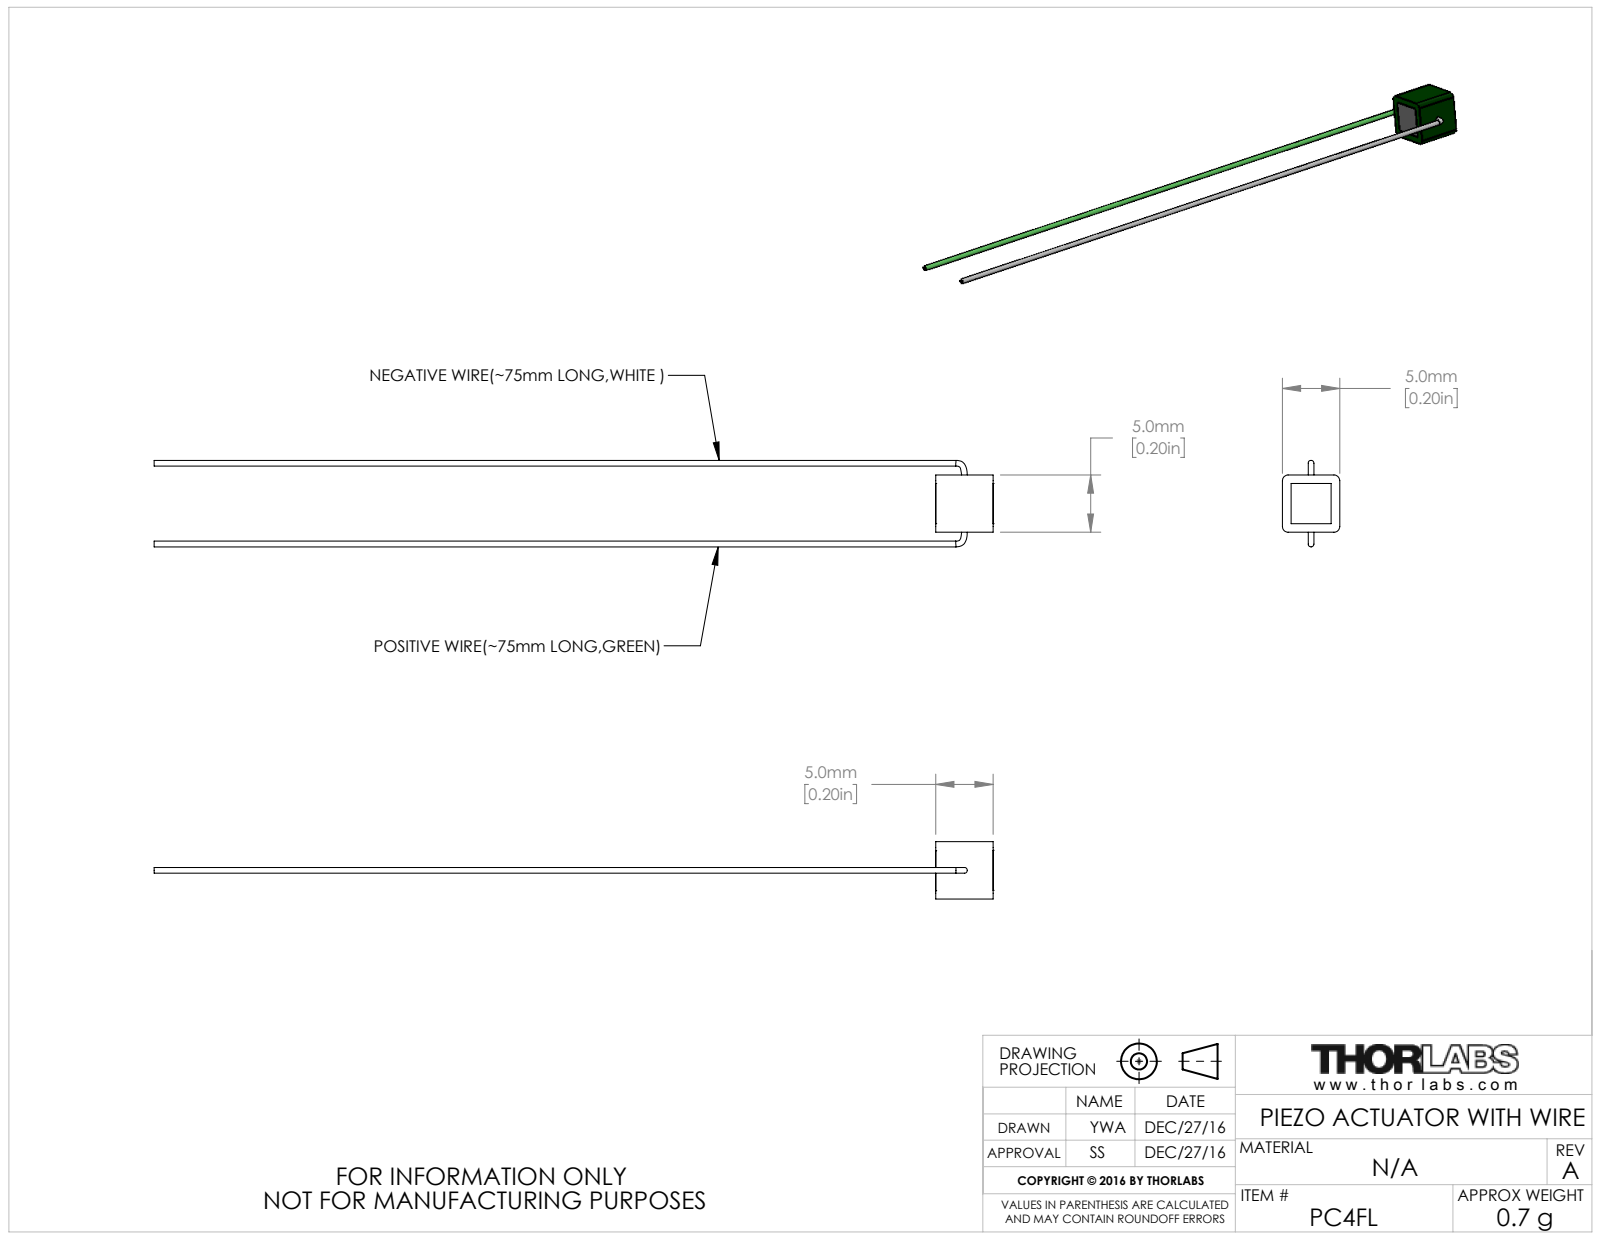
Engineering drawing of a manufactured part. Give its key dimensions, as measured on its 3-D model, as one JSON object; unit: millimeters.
{"part_name": "CTN009985", "step_written_by": "SolidWorks 2016 (AUTOMOTIVE_DESIGN)", "units": "millimeters", "bodies": {"solids": 1, "faces": 30, "planar": 18, "cylindrical": 4, "other": 8}, "overall_size": [73.26, 7.55, 5], "volume_mm3": 152, "surface_area_mm2": 370, "partial_cylinders_radius": [[0.5, 4]], "face_to_face_distances": [5, 5.01, 5.02, 73.26, 73.25, 68.25, 68.24, 0.75, 4.25, 3.5]}
